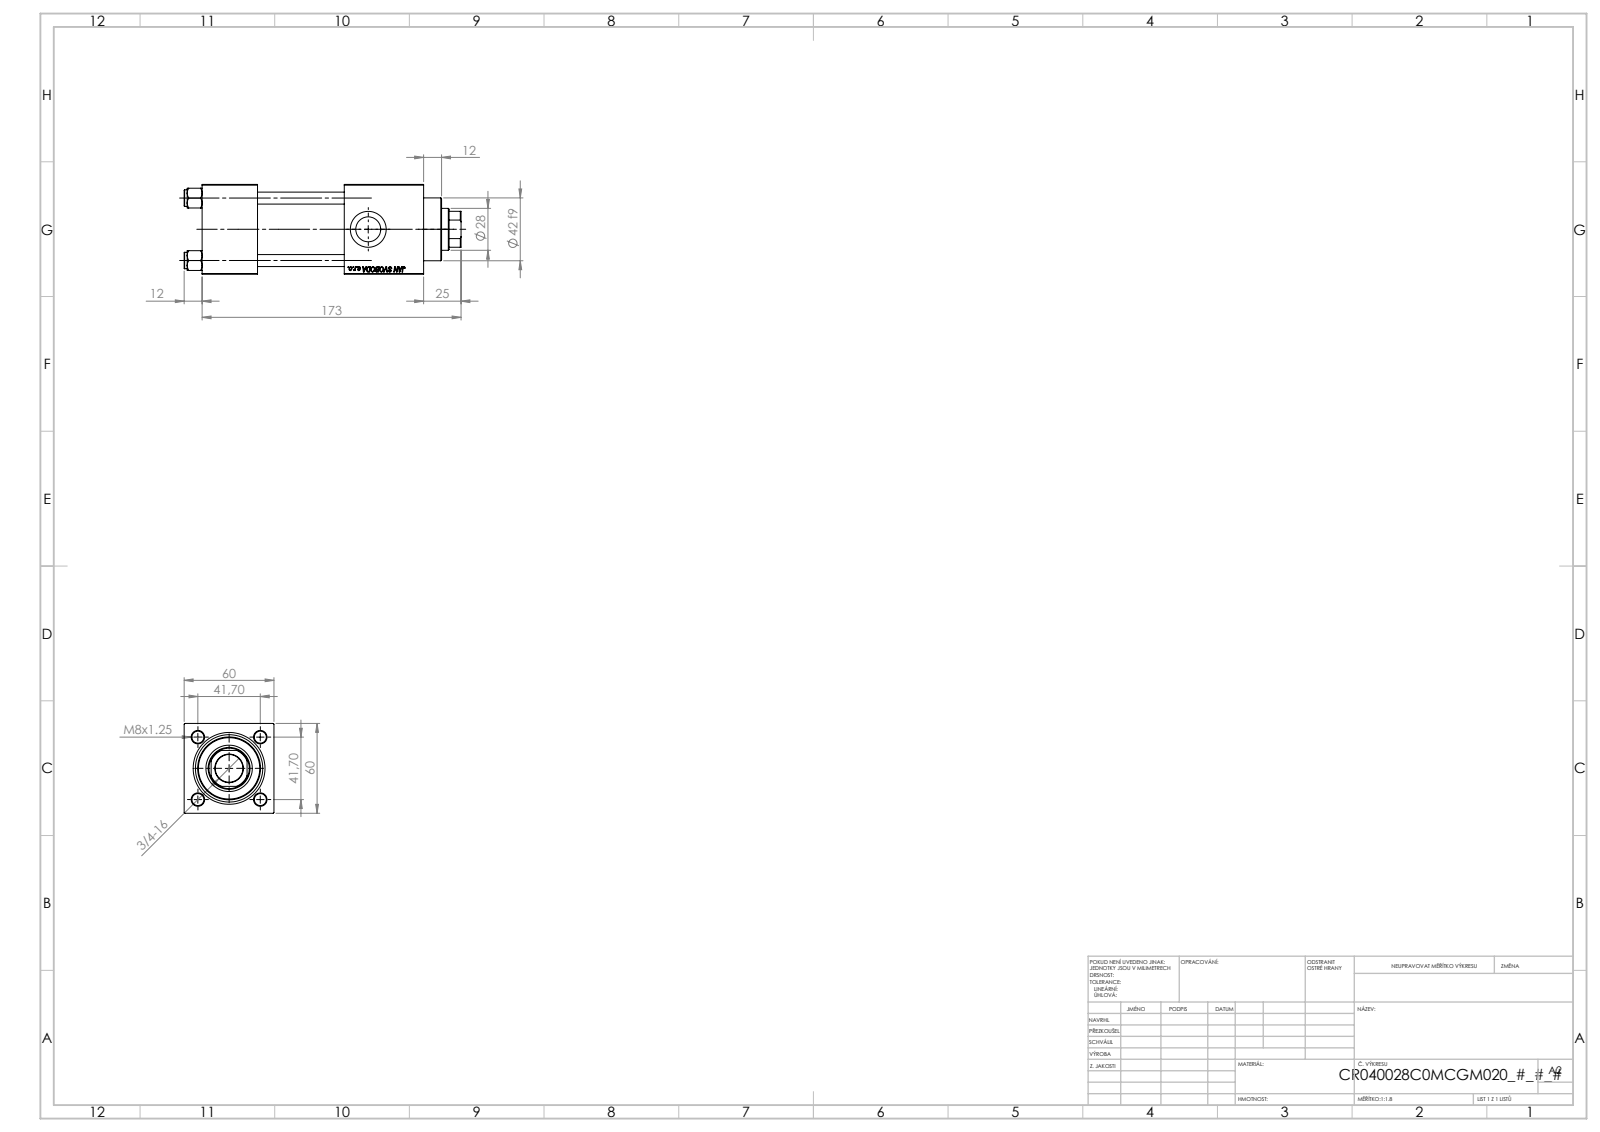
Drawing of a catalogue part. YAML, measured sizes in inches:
part_name: "V215_VC_A; NUT_M5_C; V215CR_C_Body; V215CR_C_TYCINKA (+1 more)"
step_written_by: "SolidWorks 2019 (CONFIG_CONTROL_DESIGN)"
units: inches
bodies: {solids: 11, faces: 1149, planar: 526, cylindrical: 87, other: 536}
overall_size: [7.283, 2.362, 2.362]
volume: 25.88
surface_area: 172.7
round_holes:
  - {diameter: 0.315, count: 4}
  - {diameter: 0.276, count: 2}
  - {diameter: 0.656, count: 2}
  - {diameter: 0.945, count: 2}
  - {diameter: 0.728, count: 1}
  - {diameter: 1.102, count: 1}
  - {diameter: 1.22, count: 1}
  - {diameter: 1.575, count: 1}
  - {diameter: 1.772, count: 1}
round_bosses_or_shafts:
  - {diameter: 0.433, count: 4}
  - {diameter: 1.811, count: 1}
  - {diameter: 1.654, count: 1}
partial_cylinders:
  - {radius: 0.531, count: 1}
face_to_face_distances: [2.362, 1.457, 2.283, 3.74, 2.087, 4.697, 3.24, 0.957, 5.827, 4.37]
hole_center_spacings: [1.161, 1.642, 2.322]
